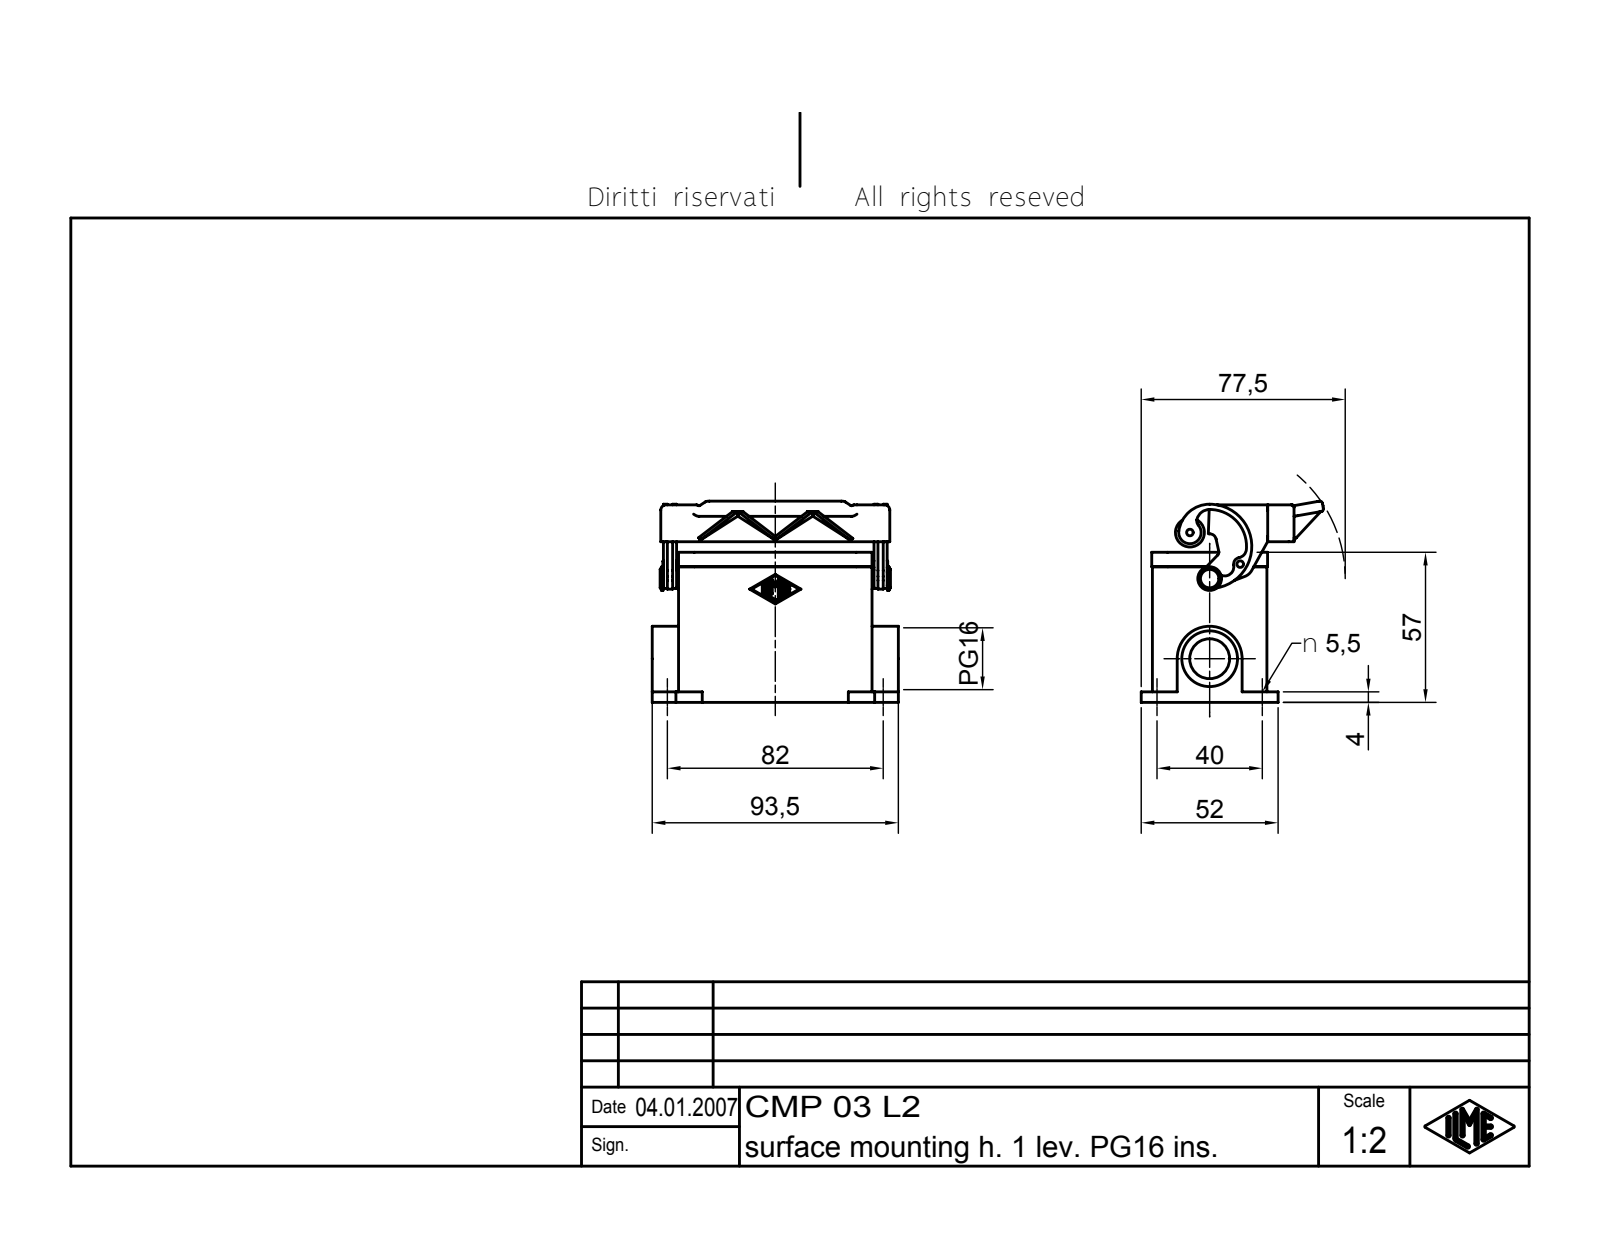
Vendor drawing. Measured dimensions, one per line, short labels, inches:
name: CMP 03 L2
written by: Autodesk Inventor 7 (AUTOMOTIVE_DESIGN)
unit: in
bodies: 4 solids, 431 faces (163 planar, 123 cylindrical, 145 other)
size: 3.681 × 3.009 × 2.724
volume: 5.201 in³; area: 72.12 in²
holes: 4× ⌀0.217, 1× ⌀0.079, 1× ⌀0.597, 1× ⌀0.833
bosses: 1× ⌀0.433, 1× ⌀0.354, 1× ⌀0.197, 1× ⌀0.118, 1× ⌀0.098
rounds: 14× R0.015, 12× R0.079, 8× R0.236, 7× R0.039, 5× R0.059, 4× R0.118, 3× R0.098, 2× R0.138
face distances: 0.118, 1.594, 0.157, 1.713, 1.476, 0.463, 0.344, 2.431, 2.028, 1.87
hole spacings: 1.575, 3.228, 3.592, 1.486
